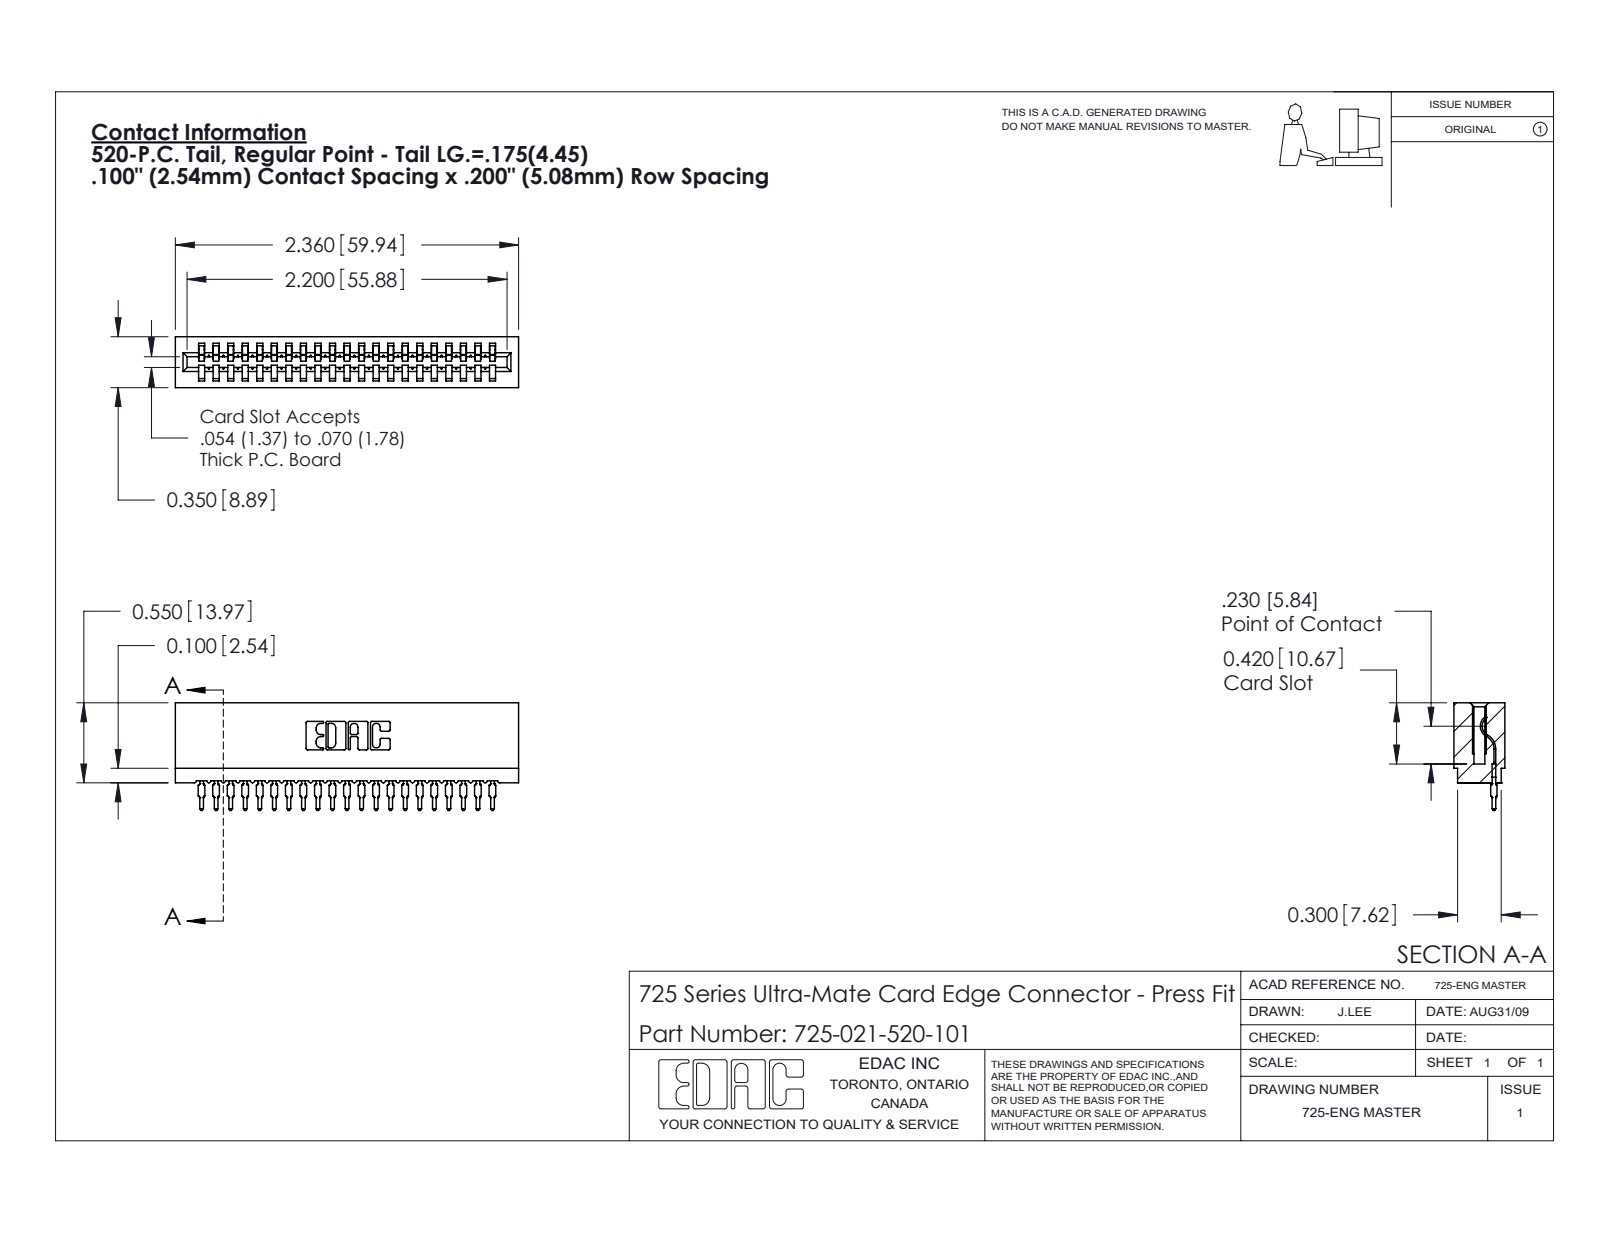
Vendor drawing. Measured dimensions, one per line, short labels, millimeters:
name: 725-021-520-101; 745-292-001_520; 725 Part_Insulator Option - 01
written by: SolidWorks 2020 (CONFIG_CONTROL_DESIGN)
unit: mm
bodies: 22 solids, 2447 faces (1462 planar, 439 cylindrical, 546 other)
size: 59.9 × 18.8 × 8.9
volume: 4 640 mm³; area: 8 426 mm²
rounds: 42× R0.4, 42× R0.5, 22× R0.3, 6× R0.2, 6× R0.8, 4× R0.1, 4× R0.3, 3× R0.7
face distances: 5.1, 2.5, 7.6, 10.2, 12.7, 15.2, 17.8, 8.9, 20.3, 5.4
